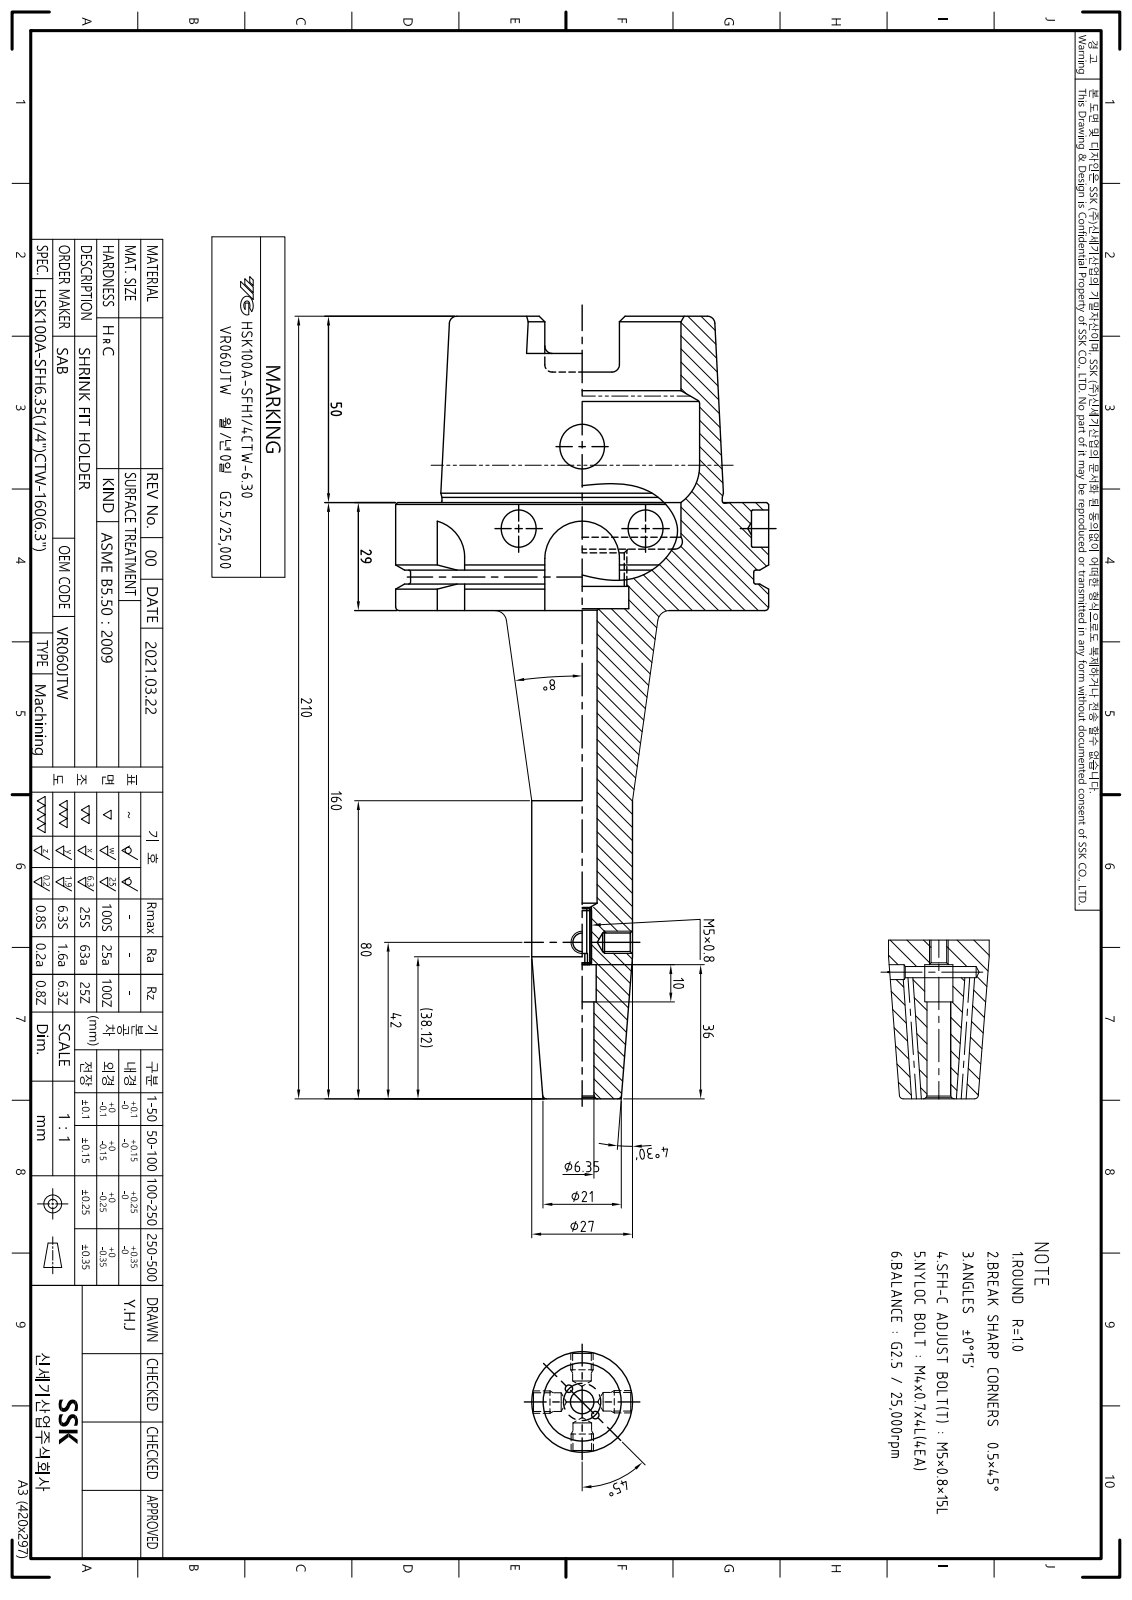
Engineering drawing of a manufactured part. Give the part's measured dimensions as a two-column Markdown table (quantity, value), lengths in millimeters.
| quantity | value |
| --- | --- |
| part name | HSK100A-SFH6.35CTW-160 |
| STEP written by | Autodesk Inventor 2022 (AUTOMOTIVE_DESIGN) |
| units | millimeters |
| bodies | 1 solid, 120 faces (38 planar, 37 cylindrical, 45 other) |
| overall size | 210 × 100 × 100 |
| volume | 332 159 mm³ |
| surface area | 63 915 mm² |
| round holes (diameter × count) | 2.5 × 2, 4.3 × 1, 6.35 × 1, 7.55 × 1, 8 × 1, 10 × 1, 12 × 1, 22.38 × 1, 25 × 1, 53 × 1, 63 × 1 |
| round bosses / shafts (diameter × count) | 100 × 1, 92 × 1, 75.41 × 1, 27 × 1 |
| partial cylindrical surfaces (radius × count) | 2 × 6, 4.88 × 4, 10 × 4 |
| main face-to-face distances | 29, 12.5, 16.5, 62.5, 50, 79, 78.5, 28.5, 16, 0.5 |
